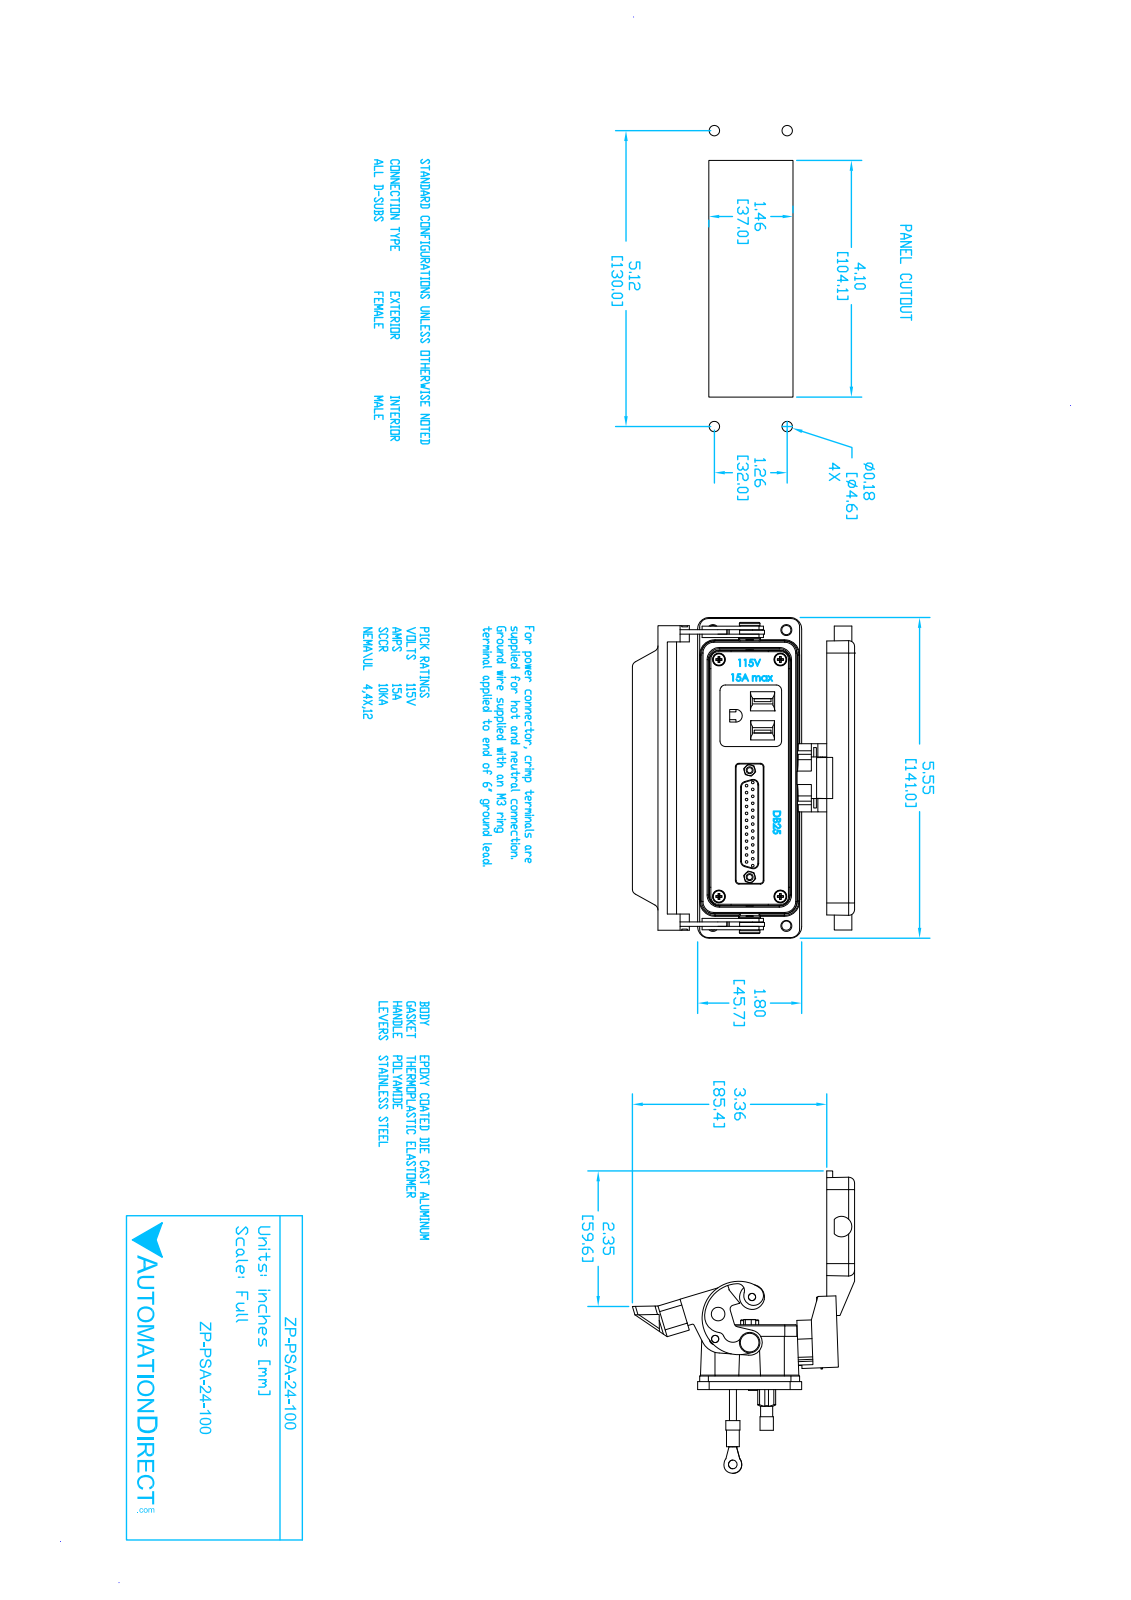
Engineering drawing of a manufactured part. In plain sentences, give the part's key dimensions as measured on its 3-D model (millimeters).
The part is named "ZP-PSA-24-100". Its 3-D file was written by "SolidWorks 2017 (AUTOMOTIVE_DESIGN)". It is 1 solid with 1807 faces: 931 planar, 548 cylindrical and 328 other. Overall it measures 142.5 by 133 by 96.7 millimeters. Its volume is 115 000 cubic millimeters and its surface area 80 260 square millimeters. Round holes: 22 of diameter 1.1, 6 of diameter 4.1, 4 of diameter 2.5, 4 of diameter 3.7, 4 of diameter 4.8, 3 of diameter 1.1, 2 of diameter 2.3, 2 of diameter 3, 2 of diameter 3.1, 2 of diameter 3.3, 2 of diameter 3.4, 1 of diameter 1.9. Round bosses or shafts: 25 of diameter 1, 4 of diameter 5.7, 4 of diameter 5.6, 4 of diameter 3, 2 of diameter 5.8, 2 of diameter 5.3, 2 of diameter 4.4, 2 of diameter 2.8. Partial cylindrical surfaces (rounded edges, fillets, slot ends): 16 of radius 0.6, 16 of radius 2.5, 12 of radius 0.3, 12 of radius 0.8, 12 of radius 3.8, 10 of radius 0.5, 8 of radius 2.4, 7 of radius 0.4. The main face-to-face distances are 18.1, 16.8, 2.9, 1.2, 40.4, 0.5, 3.4, 6, 128.4, 38.8. The hole center spacings are 3, 15.2, 12.2, 3.2, 6.1, 9.1, 8, 18.3.
